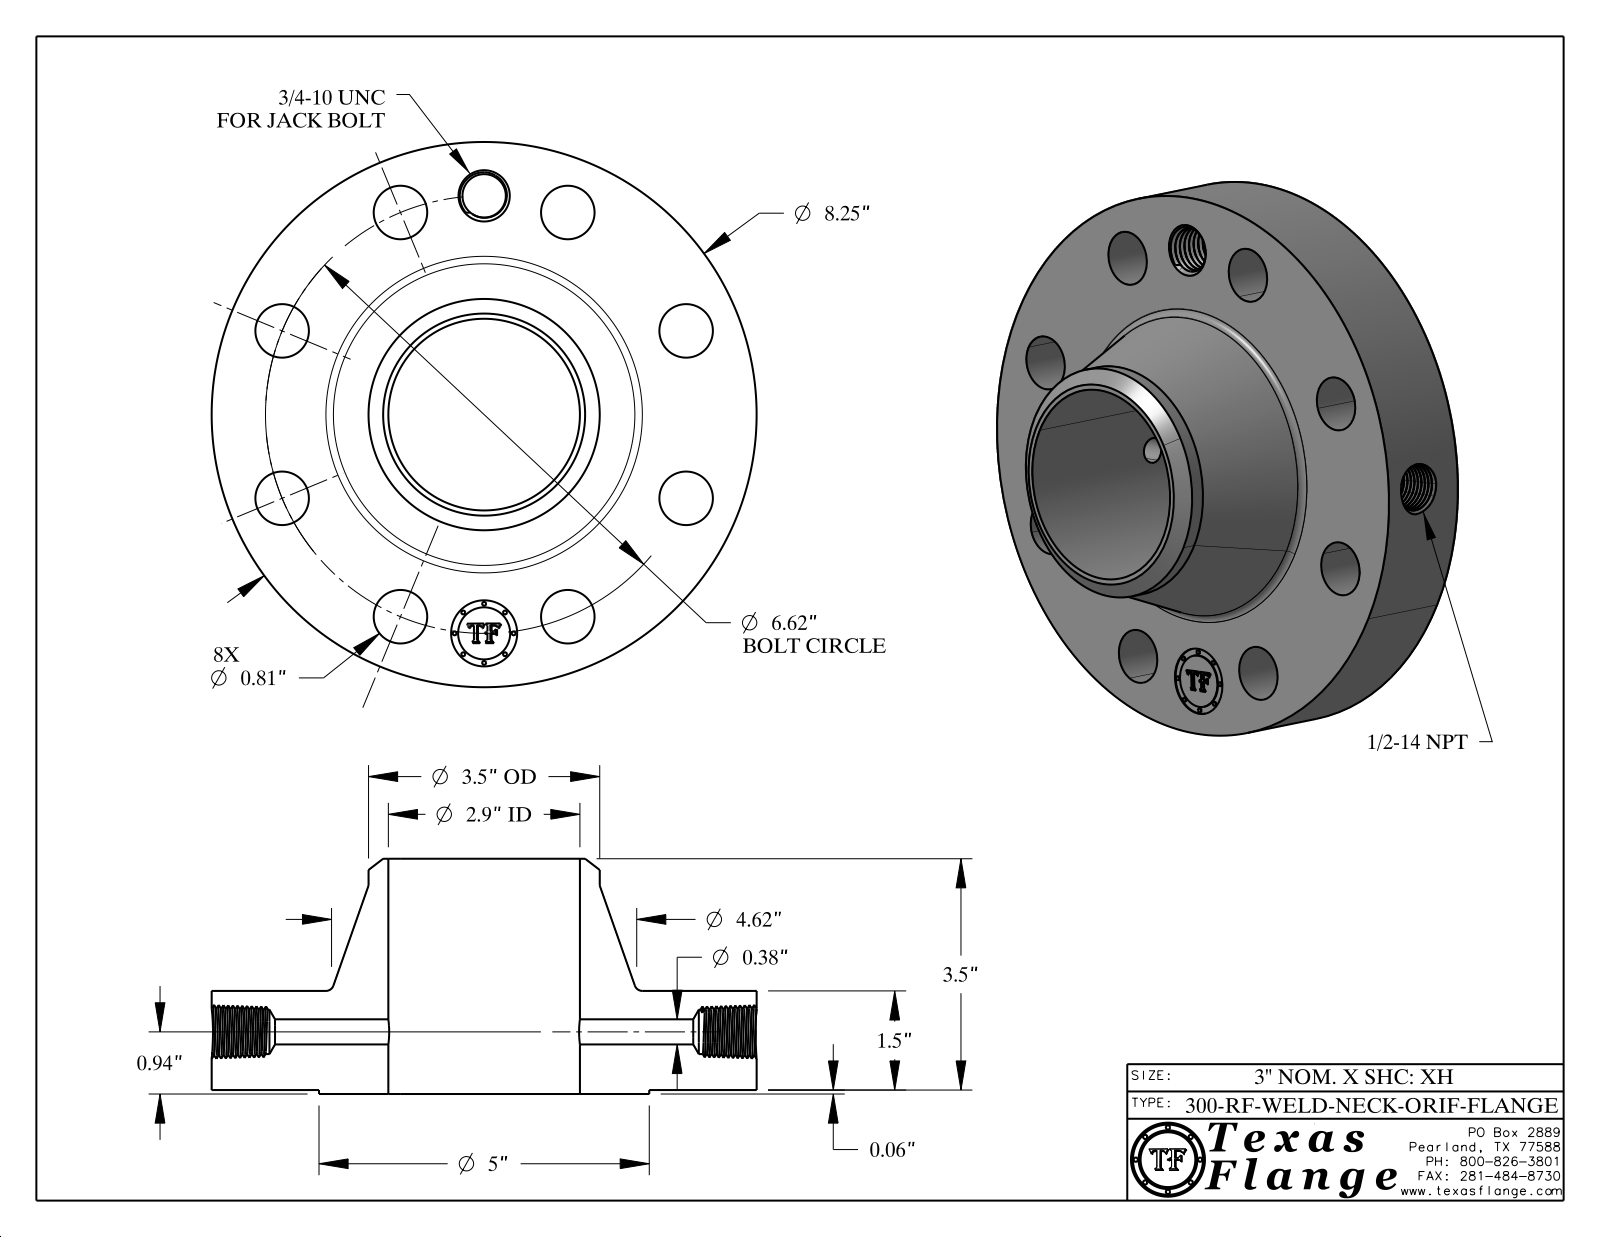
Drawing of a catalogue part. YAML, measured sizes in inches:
part_name: "300-RF-WELD-NECK"
step_written_by: "CATIA V5 STEP AP214 (AUTOMOTIVE_DESIGN)"
units: inches
bodies: {solids: 1, faces: 769, planar: 369, cylindrical: 92, other: 308}
overall_size: [8.25, 8.25, 3.56]
volume: 74.4
surface_area: 220.1
round_holes:
  - {diameter: 0.81, count: 8}
  - {diameter: 0.38, count: 1}
  - {diameter: 0.656, count: 1}
  - {diameter: 0.672, count: 1}
  - {diameter: 1, count: 1}
  - {diameter: 2.9, count: 1}
round_bosses_or_shafts:
  - {diameter: 0.061, count: 8}
  - {diameter: 8.25, count: 1}
  - {diameter: 5, count: 1}
  - {diameter: 3.5, count: 1}
  - {diameter: 0.788, count: 1}
face_to_face_distances: [1.5, 0.06, 1.56, 3.56, 3.5, 2, 0.015, 1.545, 1.485, 2.015]
hole_center_spacings: [3.31, 4.681, 6.116, 6.62, 1.291, 2.533, 2.533, 3.678]
